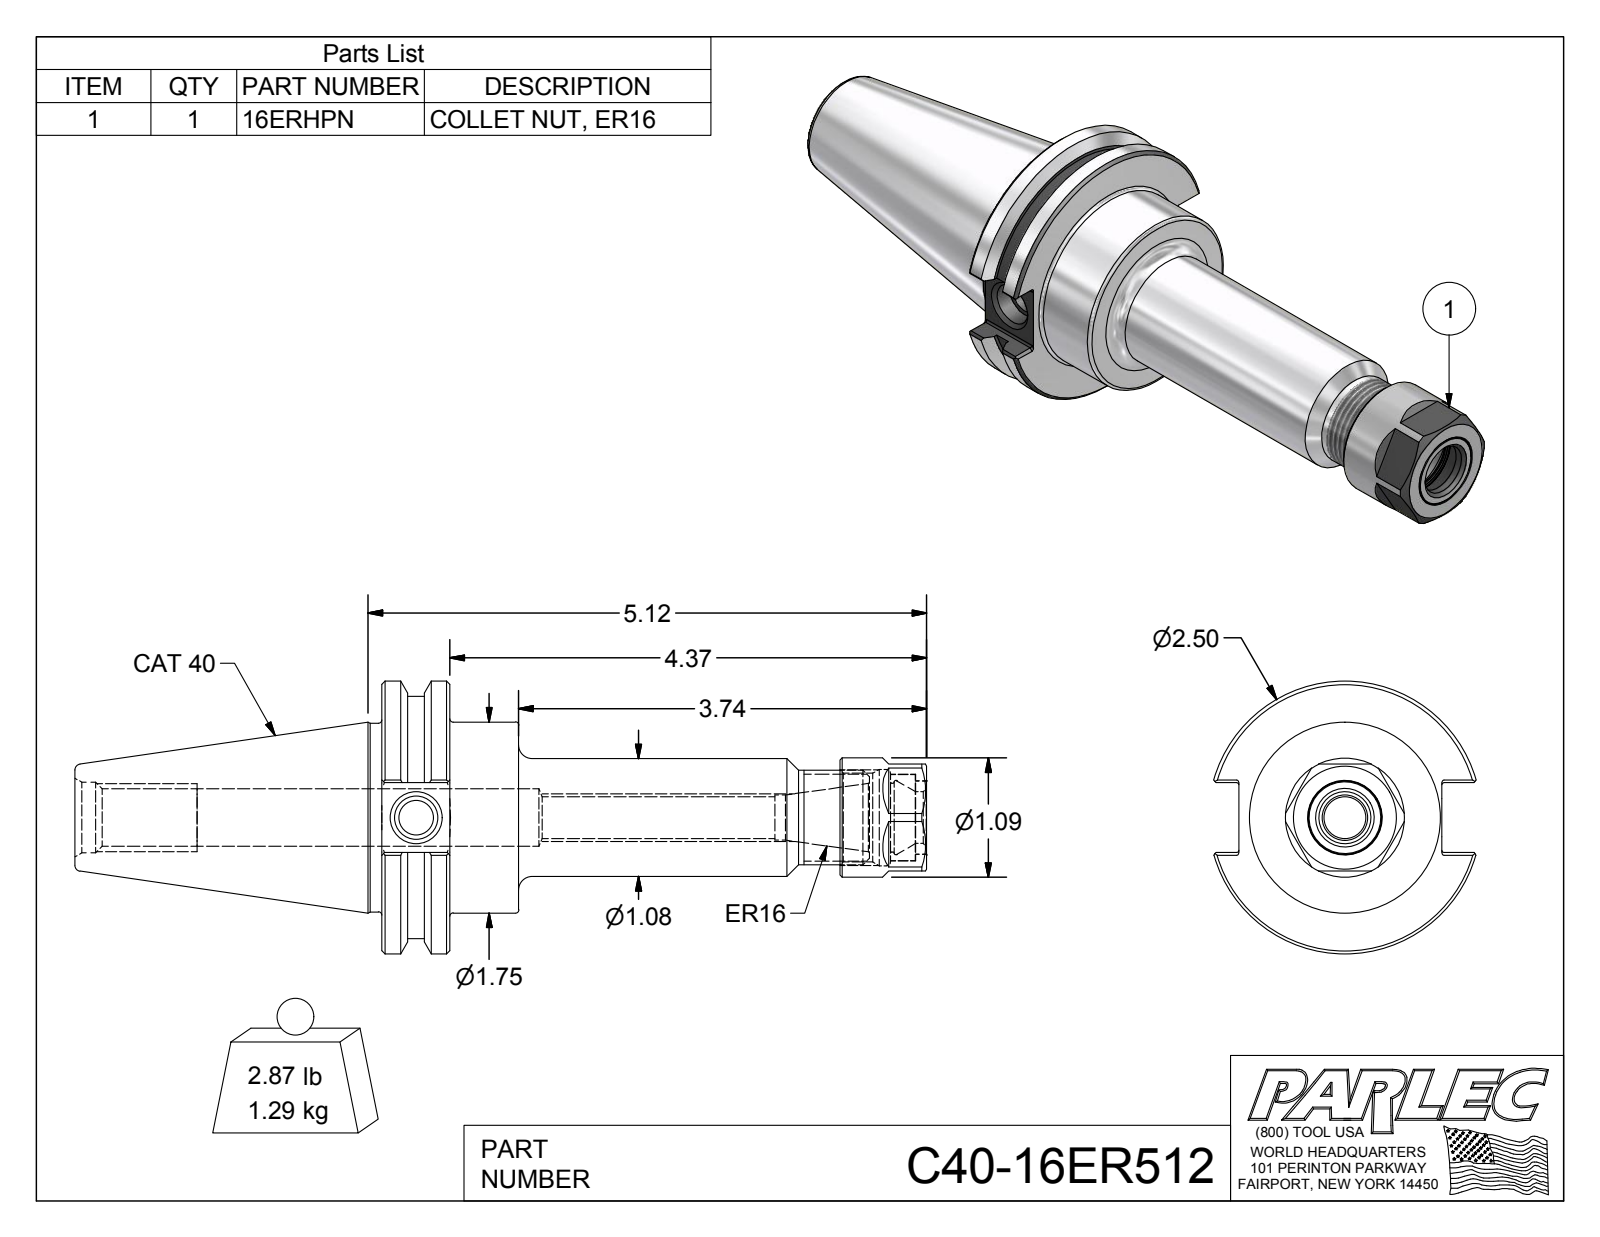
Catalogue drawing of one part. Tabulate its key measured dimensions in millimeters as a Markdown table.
| quantity | value |
| --- | --- |
| part name | C40-16ER512; C40-16ER5-1; 16ERHPN |
| STEP written by | Autodesk Inventor 2012 (AUTOMOTIVE_DESIGN) |
| units | millimeters |
| bodies | 3 solids, 130 faces (53 planar, 39 cylindrical, 38 other) |
| overall size | 198.3 × 63.5 × 61 |
| volume | 165 800 mm³ |
| surface area | 37 120 mm² |
| round holes (diameter × count) | 8 × 1, 9.7 × 1, 10.1 × 1, 10.5 × 1, 12 × 1, 13.4 × 1, 13.4 × 1, 16 × 1, 16.5 × 1, 17.1 × 1, 17.3 × 1, 20.2 × 1 |
| round bosses / shafts (diameter × count) | 63.5 × 1, 56.4 × 1, 44.5 × 1, 43.9 × 1, 27.7 × 1, 27.4 × 1, 22 × 1, 20.1 × 1 |
| partial cylindrical surfaces (radius × count) | 0.5 × 12 |
| main face-to-face distances | 15.9, 31.9, 16, 24.9, 126.9, 111, 95, 4.3, 20.6, 106.7 |
